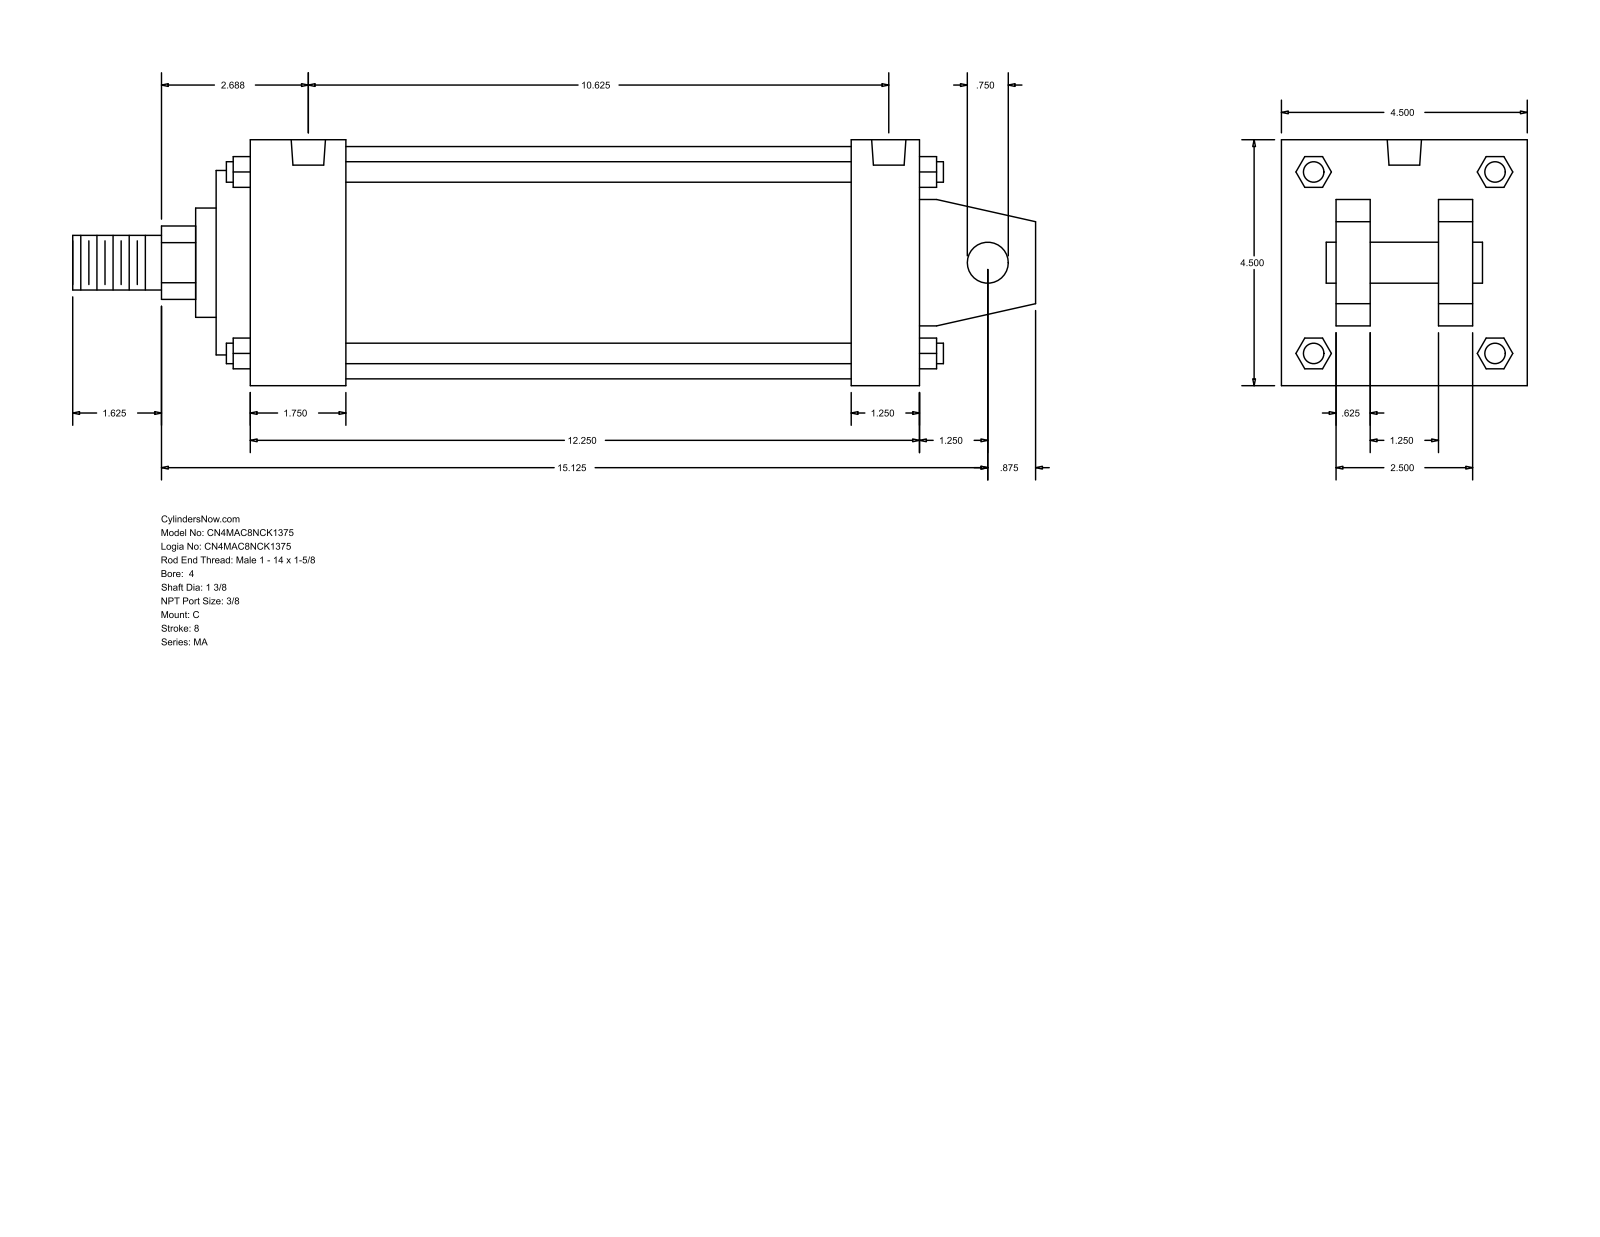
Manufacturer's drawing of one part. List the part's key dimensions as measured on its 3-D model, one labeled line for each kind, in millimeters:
Part name (STEP PRODUCT): MA_C__0400_1.375
STEP written by: GSSL Pune (CONFIG_CONTROL_DESIGN)
Units: millimetres
Bodies: 0 solids, 141 faces (109 planar, 32 cylindrical, 0 other)
Overall size (bounding box): 447.68 × 114.3 × 114.3
Round holes (diameter × count): ⌀11.11 ×4, ⌀15.93 ×2
Round bosses / shafts (diameter × count): ⌀9.53 ×4, ⌀107.95 ×1, ⌀85.72 ×1, ⌀50.8 ×1, ⌀34.92 ×1, ⌀25.4 ×1, ⌀19.05 ×1
Partial cylindrical surfaces — rounded edges, fillets, slot ends (radius × count): R17.06 ×1
Main face-to-face distances: 114.3, 15.87, 311.16, 73.03, 41.27, 25.4, 88.9, 47.63, 327.03, 295.28
Hole centre spacings: 260.35, 4.76, 4.77, 265.11, 265.12, 269.88
